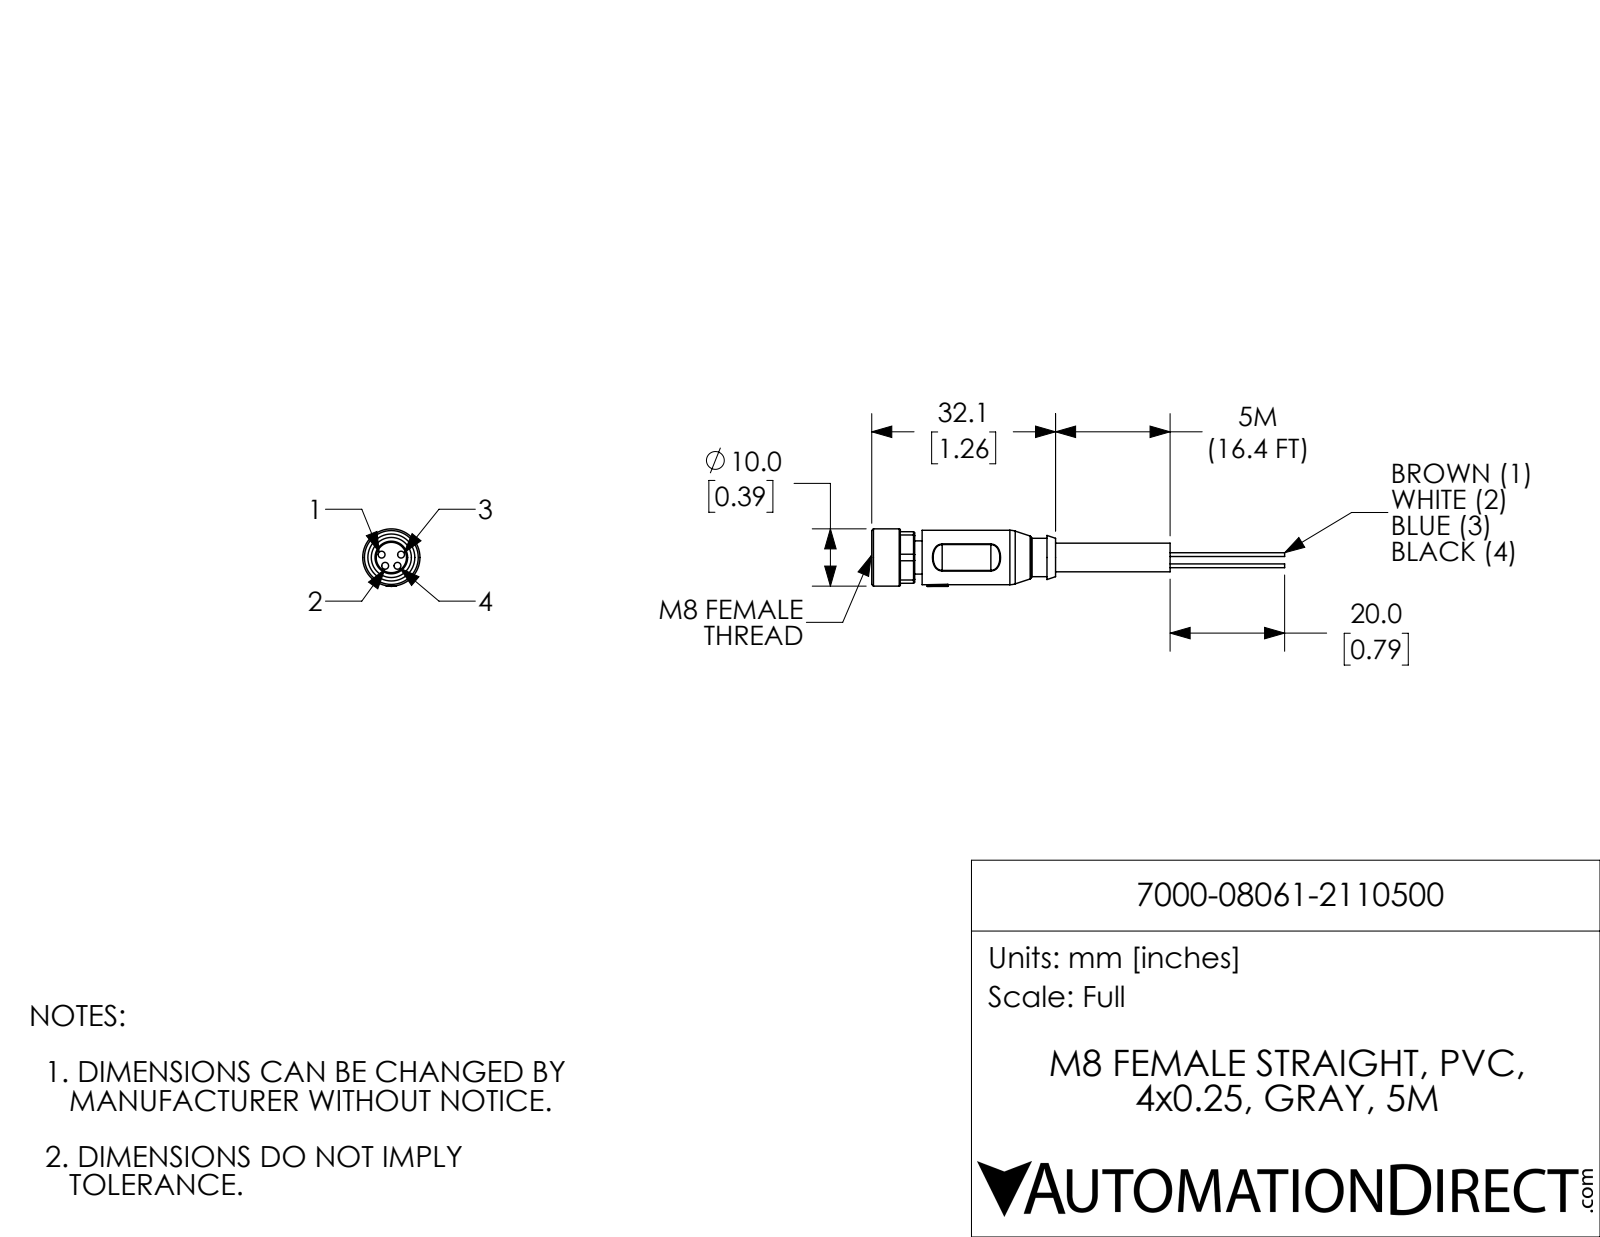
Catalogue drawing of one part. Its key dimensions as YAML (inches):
part_name: "7000-08061-2110500"
step_written_by: "SolidWorks 2017 (AUTOMOTIVE_DESIGN)"
units: inches
bodies: {solids: 1, faces: 115, planar: 38, cylindrical: 46, other: 31}
overall_size: [2.839, 0.396, 0.394]
volume: 0.141
surface_area: 2.944
round_holes:
  - {diameter: 0.047, count: 4}
  - {diameter: 0.276, count: 1}
round_bosses_or_shafts:
  - {diameter: 0.026, count: 4}
  - {diameter: 0.394, count: 1}
  - {diameter: 0.374, count: 1}
  - {diameter: 0.264, count: 1}
  - {diameter: 0.228, count: 1}
  - {diameter: 0.224, count: 1}
  - {diameter: 0.197, count: 1}
partial_cylinders:
  - {radius: 0.008, count: 4}
  - {radius: 0.098, count: 4}
  - {radius: 0.193, count: 1}
  - {radius: 0.199, count: 1}
face_to_face_distances: [0.327, 0.051, 0.969, 0.354, 0.059, 0.028, 1.756, 1.705, 0.268, 0.319]
hole_center_spacings: [0.07, 0.071, 0.081, 0.133, 0.084, 0.134]
